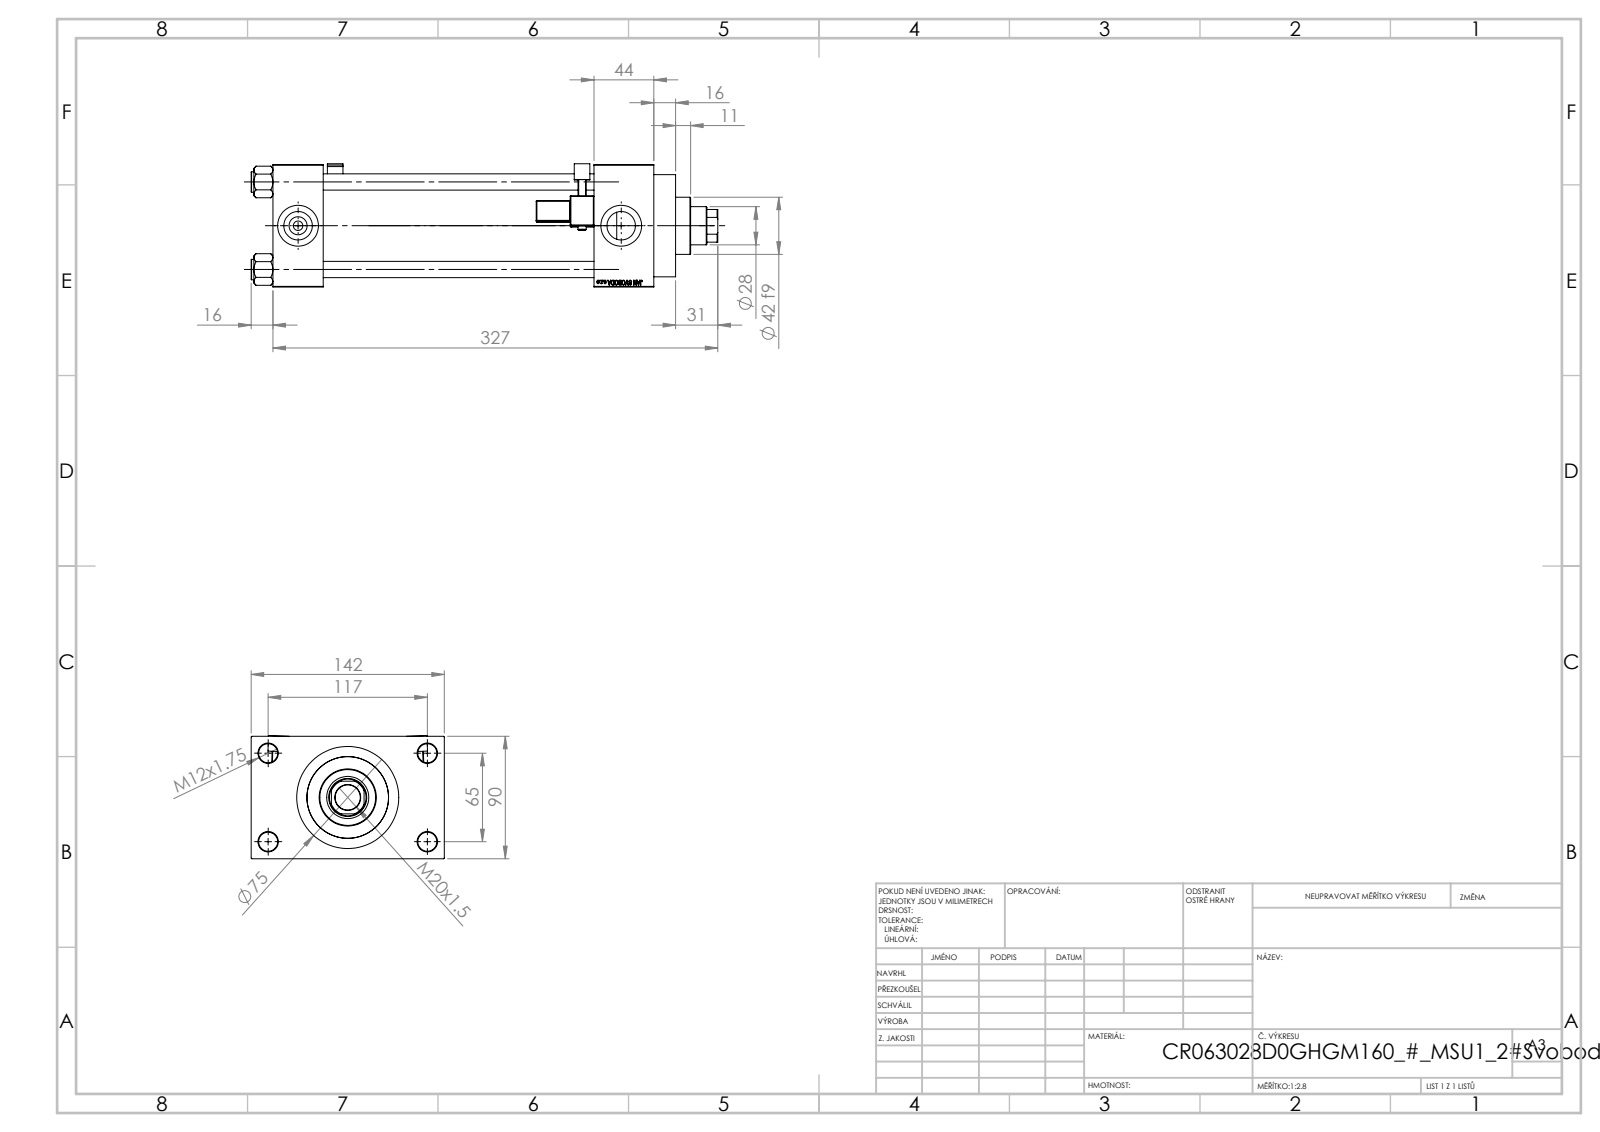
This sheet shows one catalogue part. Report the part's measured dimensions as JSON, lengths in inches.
{"part_name": "V215CR_D_TYCINKA; V215_VC_A; V215CR_VCP_D; V215CR_D_Body (+2 more)", "step_written_by": "SolidWorks 2019 (CONFIG_CONTROL_DESIGN)", "units": "inches", "bodies": {"solids": 13, "faces": 1257, "planar": 555, "cylindrical": 148, "other": 554}, "overall_size": [13.504, 5.591, 3.564], "volume_in3": 83.85, "surface_area_in2": 471.3, "round_holes": [[0.472, 4], [0.551, 4], [0.276, 2], [0.825, 2], [1.181, 2], [0.728, 1], [1.102, 1], [1.22, 1], [1.969, 1], [2.362, 1], [2.48, 1]], "round_bosses_or_shafts": [[0.591, 4], [0.236, 2], [2.953, 1], [2.717, 1], [1.654, 1]], "partial_cylinders_radius": [[0.02, 48], [0.039, 2], [0.098, 2], [0.157, 2], [0.531, 1]], "face_to_face_distances": [3.543, 7.835, 1.457, 9.291, 11.024, 9.567, 1.732, 1.024, 4.567, 0.63], "hole_center_spacings": [1.037, 1.79, 2.531, 2.635, 2.748, 3.569, 4.383, 2.559]}
